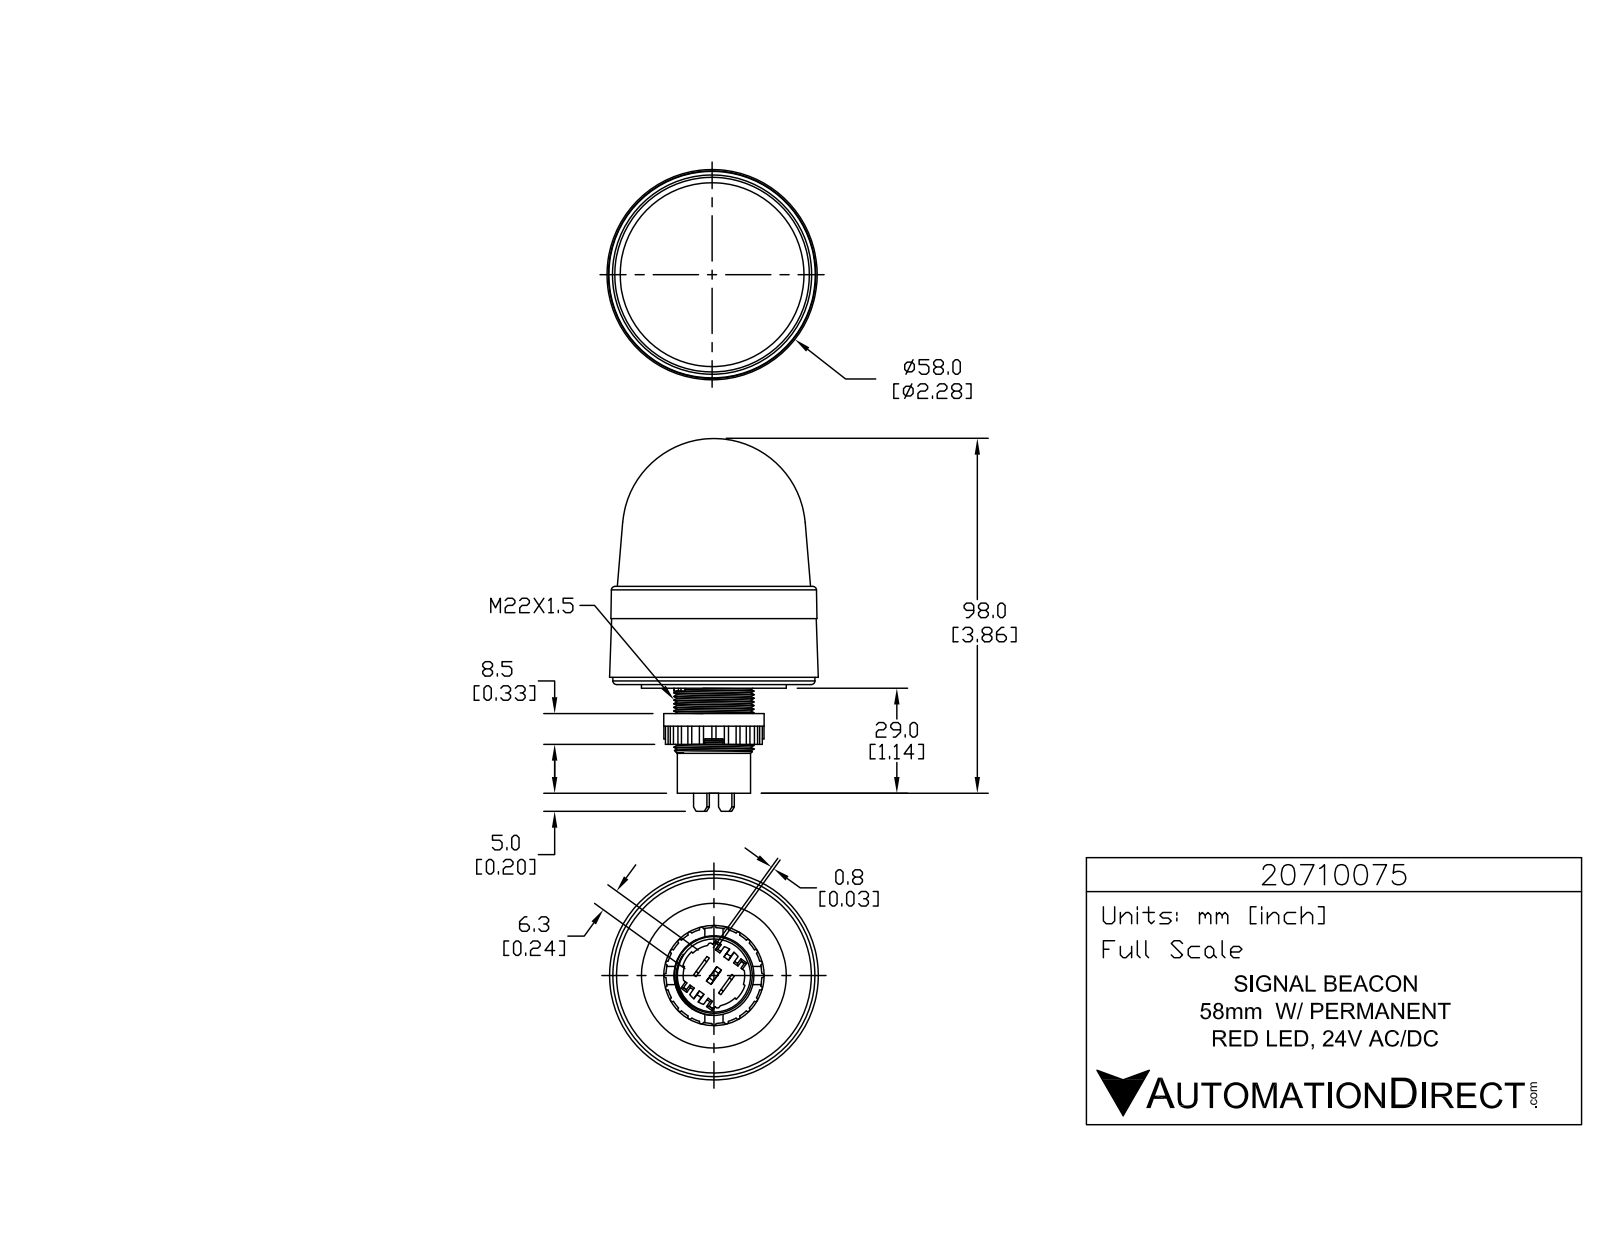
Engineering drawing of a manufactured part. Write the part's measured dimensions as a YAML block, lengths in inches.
part_name: "20710075"
step_written_by: "SolidWorks 2015 (AUTOMOTIVE_DESIGN)"
units: inches
bodies: {solids: 1, faces: 266, planar: 119, cylindrical: 120, other: 27}
overall_size: [4.051, 2.269, 2.269]
volume: 9.016
surface_area: 31.05
round_holes:
  - {diameter: 0.906, count: 1}
round_bosses_or_shafts:
  - {diameter: 2.197, count: 1}
  - {diameter: 1.575, count: 1}
  - {diameter: 1.091, count: 1}
  - {diameter: 0.866, count: 1}
  - {diameter: 0.795, count: 1}
partial_cylinders:
  - {radius: 0.023, count: 24}
  - {radius: 0.02, count: 2}
  - {radius: 0.335, count: 1}
  - {radius: 0.354, count: 1}
  - {radius: 0.522, count: 1}
face_to_face_distances: [0.039, 0.276, 0.118, 1.142, 0.335, 0.315, 1.063, 0.748, 1.024, 0.728]
